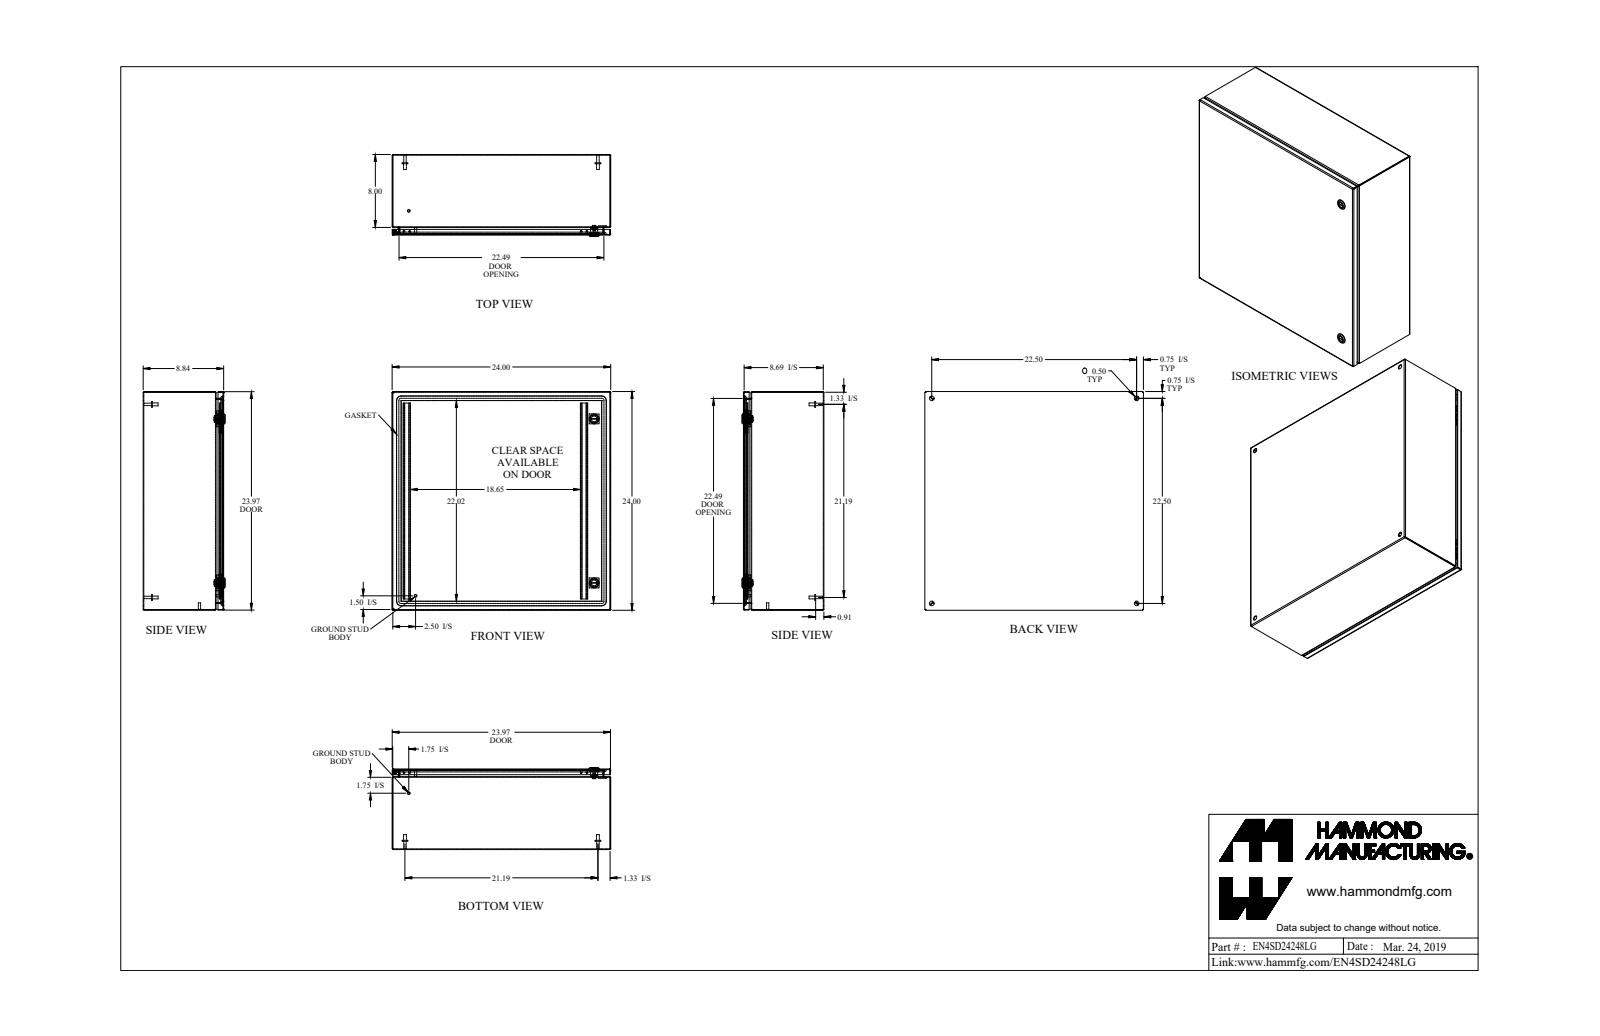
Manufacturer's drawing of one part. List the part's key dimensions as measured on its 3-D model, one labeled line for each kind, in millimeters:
Part name (STEP PRODUCT): EN4SD24248LG_Default
STEP written by: SolidWorks 2019 (CONFIG_CONTROL_DESIGN)
Units: millimetres
Bodies: 27 solids, 783 faces (386 planar, 257 cylindrical, 140 other)
Overall size (bounding box): 609.6 × 609.6 × 228.5
Volume: 2 686 000 mm³ · Surface area: 2 961 000 mm²
Round holes (diameter × count): ⌀12.7 ×4, ⌀5.9 ×2, ⌀15.9 ×2, ⌀19.9 ×2, ⌀4.4 ×1, ⌀6.1 ×1, ⌀6.1 ×1
Round bosses / shafts (diameter × count): ⌀15.9 ×4, ⌀8 ×4, ⌀6.9 ×4, ⌀27.9 ×2, ⌀13.3 ×2, ⌀7.1 ×2, ⌀6.4 ×2, ⌀11.6 ×1
Partial cylindrical surfaces — rounded edges, fillets, slot ends (radius × count): R0.9 ×20, R2.7 ×20, R1.1 ×12, R2.1 ×12, R9.7 ×12, R482.7 ×8, R0.2 ×4, R1.6 ×4
Main face-to-face distances: 1.8, 222.6, 607.8, 220.8, 224.5, 605.9, 609.6, 21.3, 201.4, 19.1
Hole centre spacings: 571.5, 808.2, 63.3, 63.3, 457.2, 515, 515.1, 547.2
